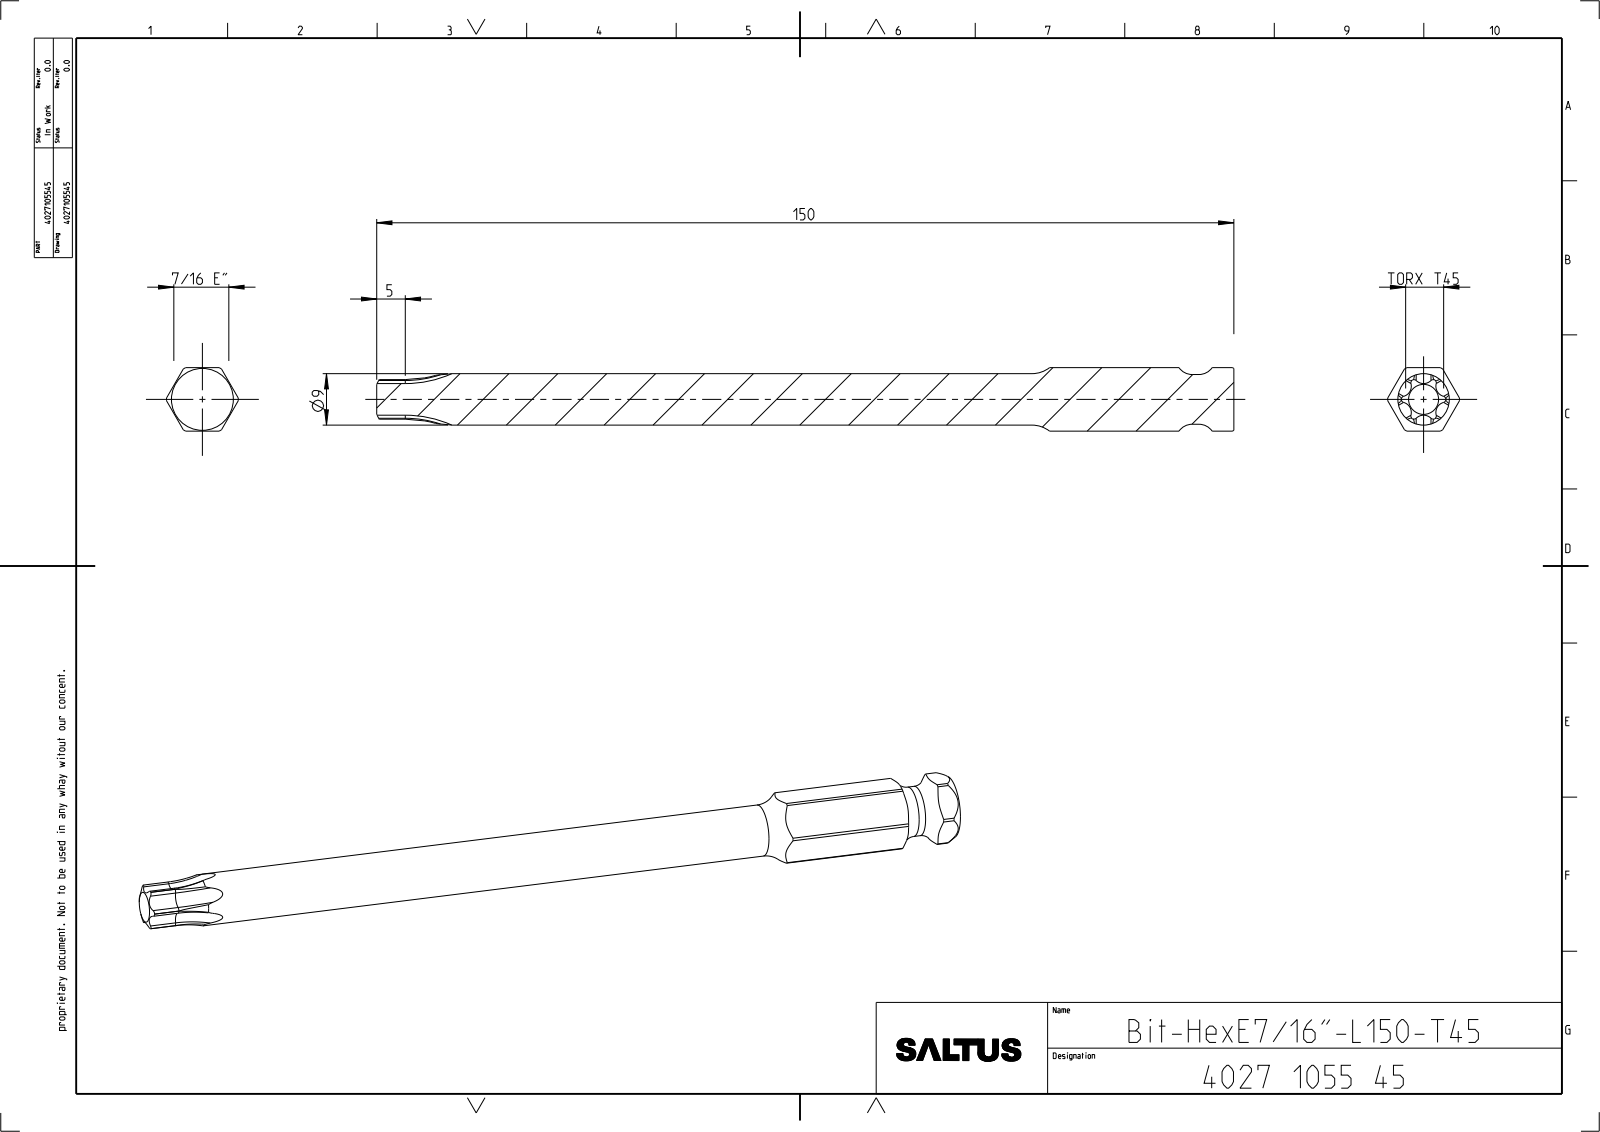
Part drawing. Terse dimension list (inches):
name: 4027105545
written by: CREO PARAMETRIC BY PTC INC, 2022414 (CONFIG_CONTROL_DESIGN)
unit: in
bodies: 1 solid, 88 faces (14 planar, 40 cylindrical, 34 other)
size: 5.906 × 0.494 × 0.437
volume: 0.636 in³; area: 7.234 in²
bosses: 1× ⌀0.354, 1× ⌀0.343
rounds: 12× R0.021, 6× R0.072, 1× R0.154, 1× R0.247
face distances: 0.437, 5.906
